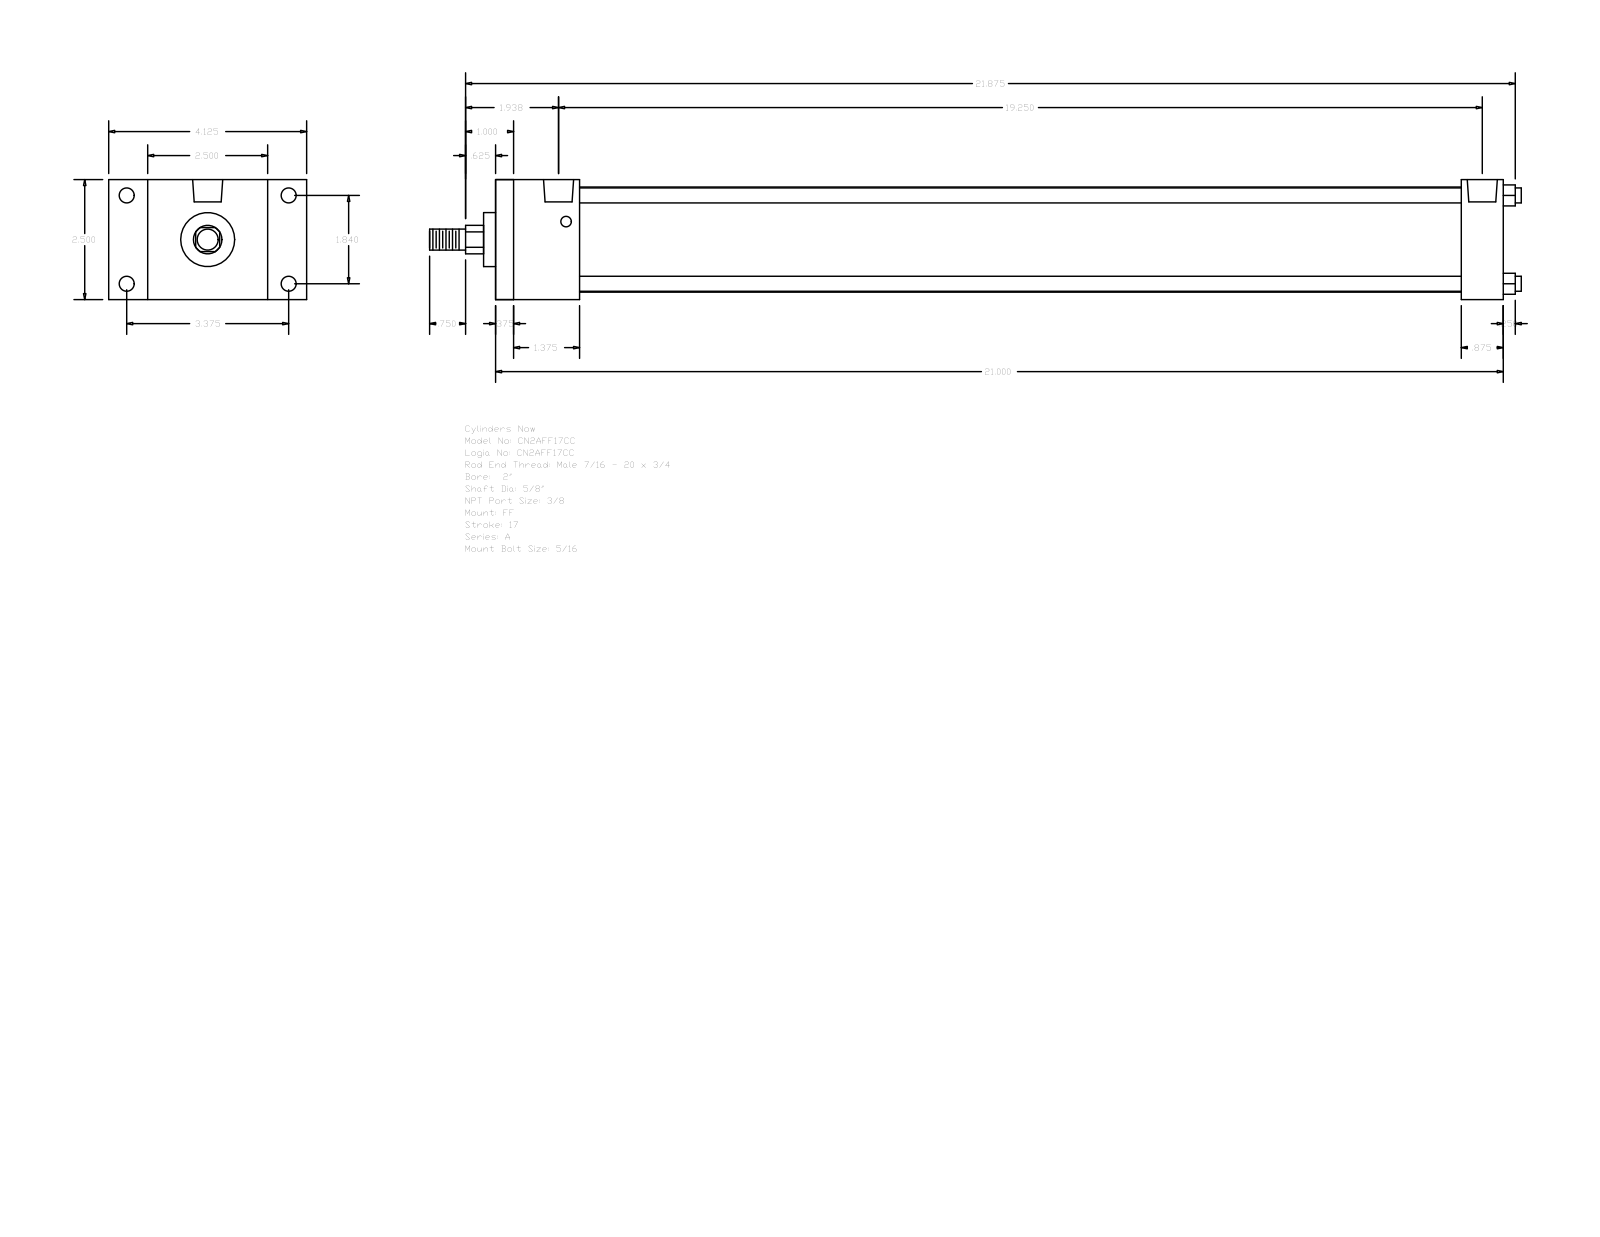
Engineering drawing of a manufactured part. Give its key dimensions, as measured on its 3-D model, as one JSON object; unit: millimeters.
{"part_name": "A_FF__0200_0.625", "step_written_by": "GSSL Pune (CONFIG_CONTROL_DESIGN)", "units": "millimeters", "bodies": {"solids": 0, "faces": 92, "planar": 64, "cylindrical": 28, "other": 0}, "overall_size": [577.85, 104.78, 63.5], "round_holes": [[5.56, 4], [7.94, 4], [15.93, 2]], "round_bosses_or_shafts": [[7.94, 4], [55.63, 1], [28.57, 1], [15.88, 1], [11.11, 1]], "partial_cylinders_radius": [[7.54, 1]], "face_to_face_distances": [63.5, 533.39, 9.52, 523.87, 34.93, 44.45, 511.17, 501.65, 466.72, 488.94], "hole_center_spacings": [46.74, 85.72, 97.63, 481, 3.97, 3.98, 484.97, 484.98]}
